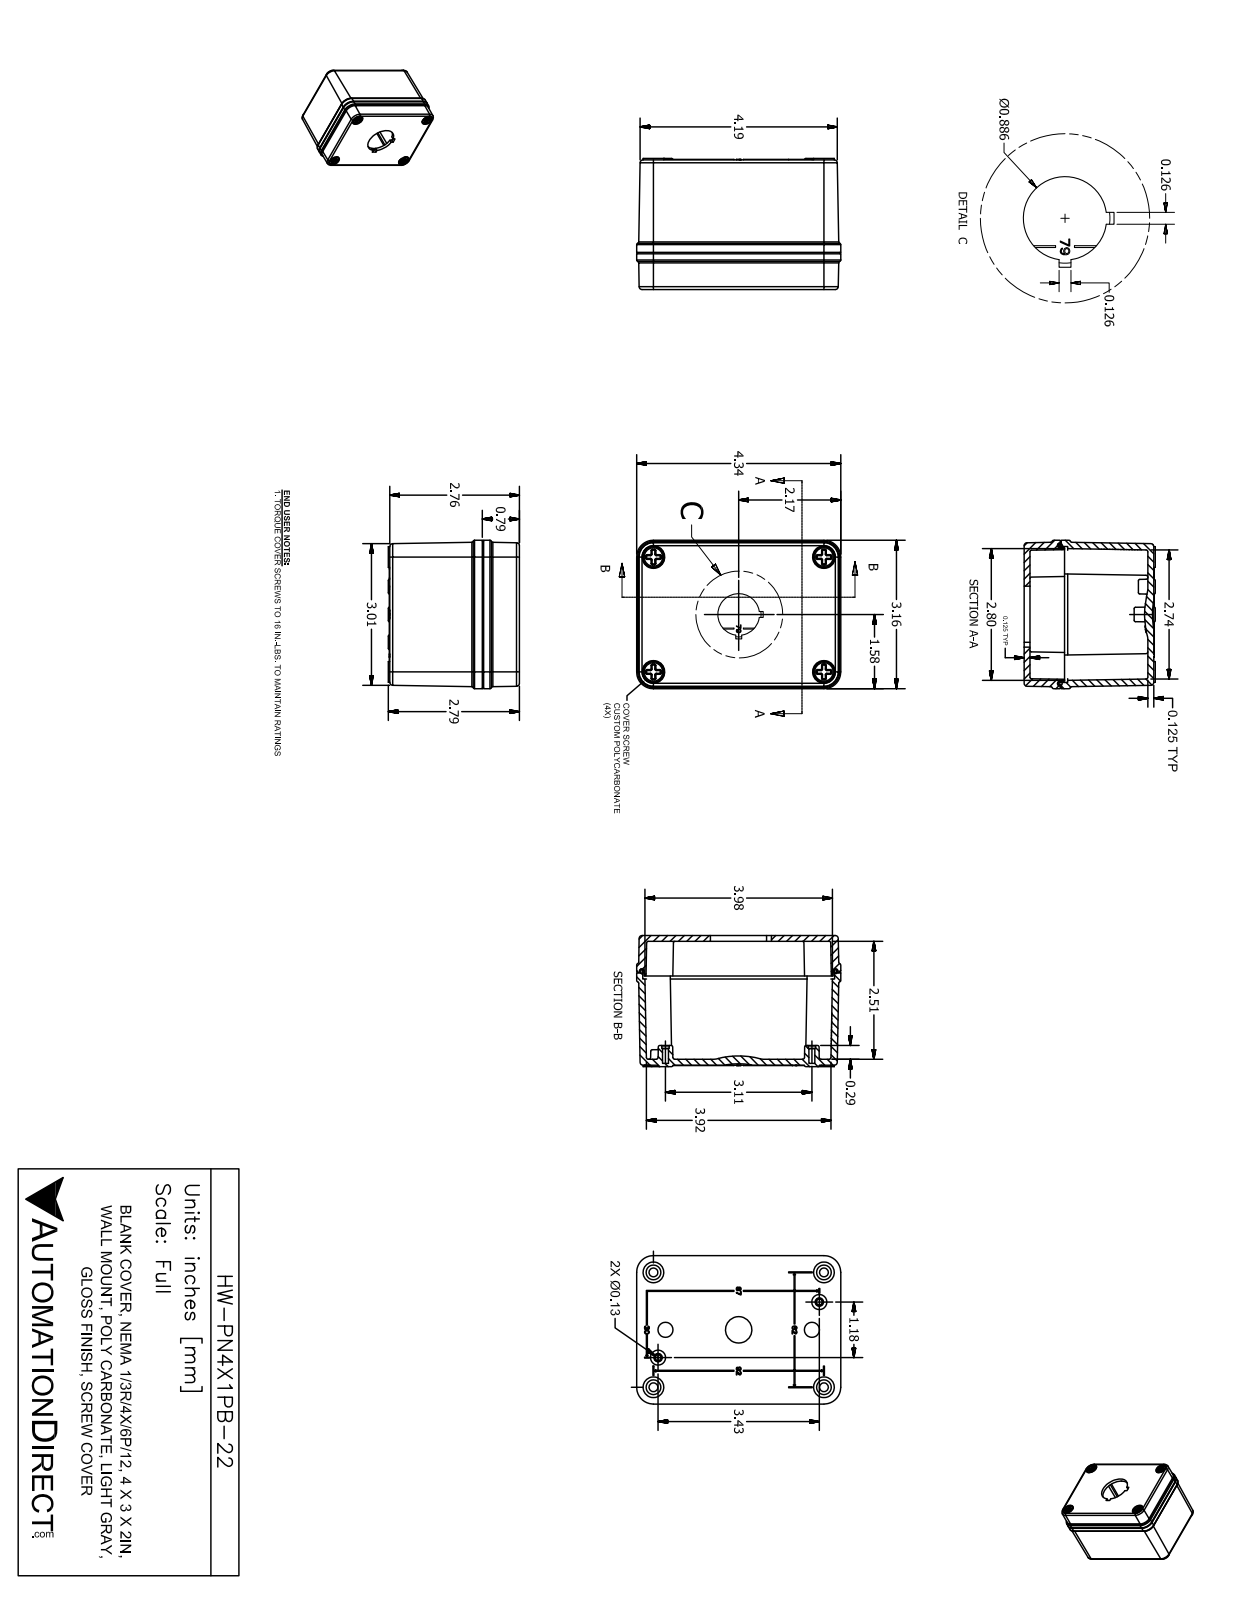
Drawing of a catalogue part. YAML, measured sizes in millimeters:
part_name: "HW-PN4X1PB-22"
step_written_by: "SolidWorks 2017 (AUTOMOTIVE_DESIGN)"
units: millimeters
bodies: {solids: 7, faces: 1040, planar: 218, cylindrical: 378, other: 444}
overall_size: [110.1, 80.2, 70.7]
volume: 164000
surface_area: 99100
round_holes:
  - {diameter: 2.5, count: 6}
  - {diameter: 4.7, count: 4}
  - {diameter: 10, count: 4}
  - {diameter: 11.7, count: 4}
  - {diameter: 22.5, count: 1}
round_bosses_or_shafts:
  - {diameter: 12.7, count: 4}
  - {diameter: 11, count: 4}
  - {diameter: 7, count: 4}
  - {diameter: 2.5, count: 2}
partial_cylinders:
  - {radius: 0.3, count: 48}
  - {radius: 0.5, count: 48}
  - {radius: 0.8, count: 16}
  - {radius: 0.4, count: 12}
  - {radius: 0.5, count: 8}
  - {radius: 0.5, count: 8}
  - {radius: 0.8, count: 8}
  - {radius: 1.6, count: 8}
face_to_face_distances: [3.4, 70, 66.5, 66.8, 63.4, 3.2, 4.1, 49.9, 46.5, 16.9]
hole_center_spacings: [55.5, 62, 62, 14.5, 90.1, 91.8, 91.9, 92]
